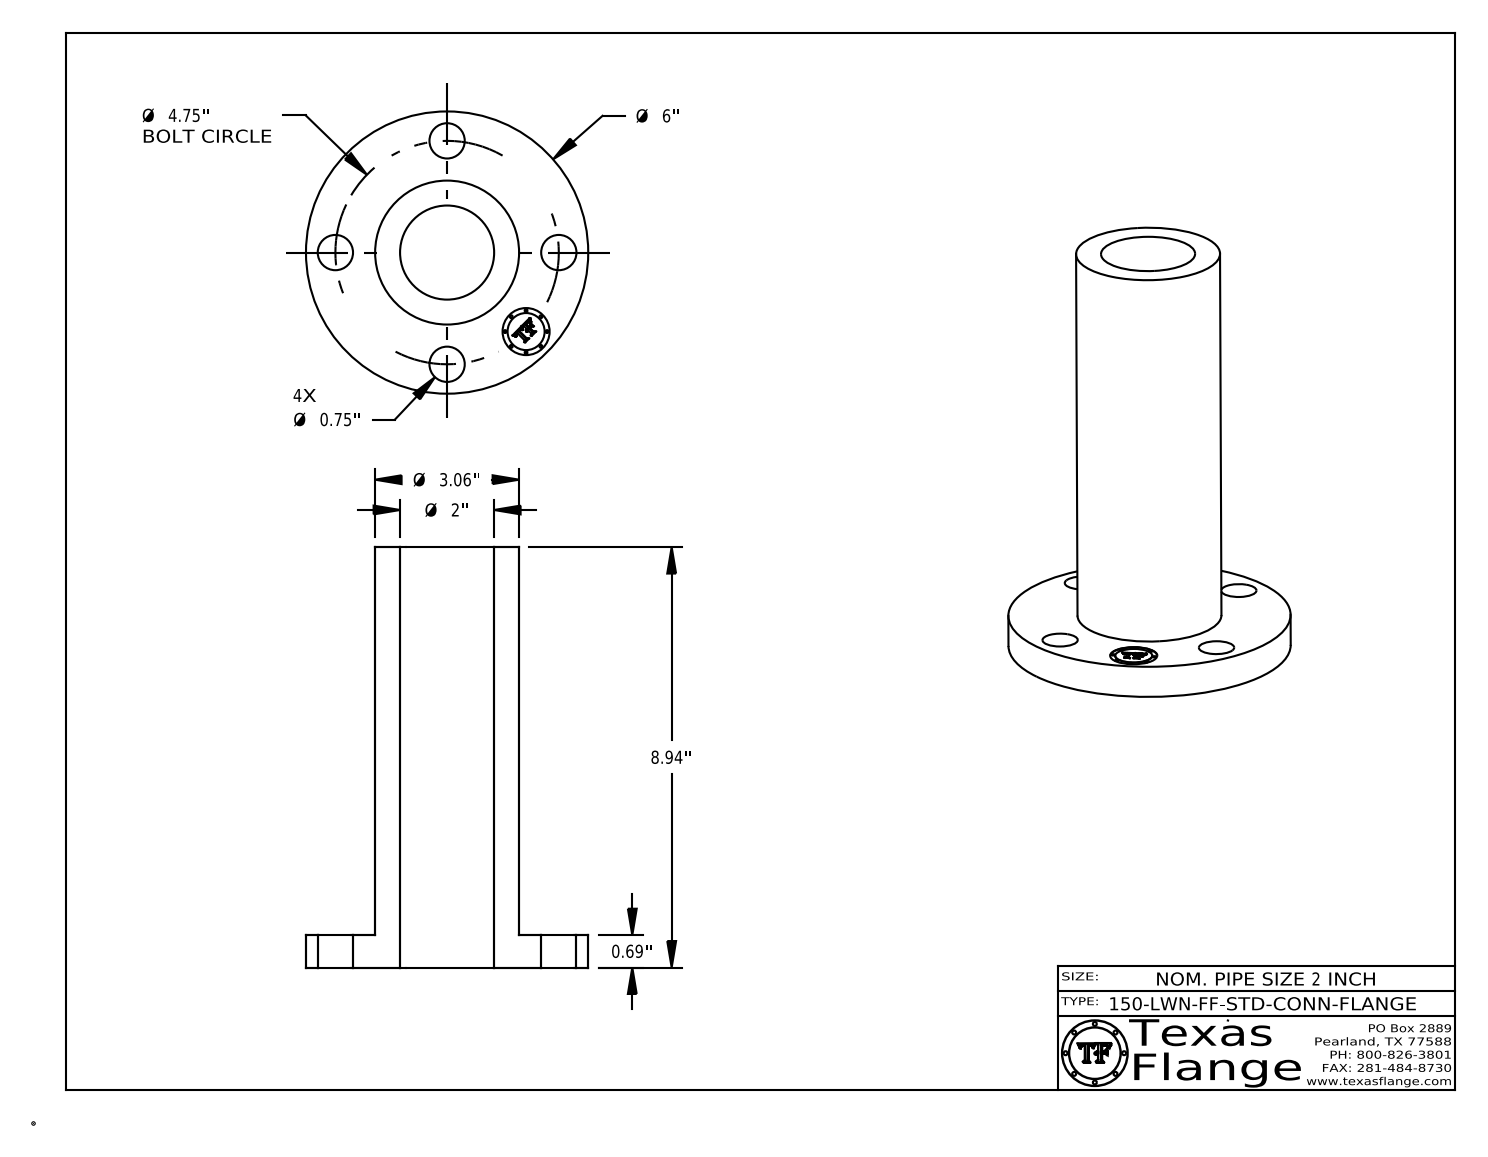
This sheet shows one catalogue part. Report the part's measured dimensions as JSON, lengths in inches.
{"part_name": "2-150-LWN-FF-STD-CONN-FLANGE", "step_written_by": "CATIA V5 STEP AP214 (AUTOMOTIVE_DESIGN)", "units": "inches", "bodies": {"solids": 1, "faces": 402, "planar": 368, "cylindrical": 34, "other": 0}, "overall_size": [8.938, 6, 6], "volume_in3": 50.82, "surface_area_in2": 201.7, "round_holes": [[0.75, 4], [1, 1], [2, 1]], "round_bosses_or_shafts": [[0.061, 8], [6, 1], [3.06, 1], [0.788, 1]], "face_to_face_distances": [0.687, 8.937, 8.25, 0.683, 8.255, 0.298, 0.292, 0.054, 0.193, 0.248], "hole_center_spacings": [2.375, 3.359, 1.818, 4.389, 4.75]}
